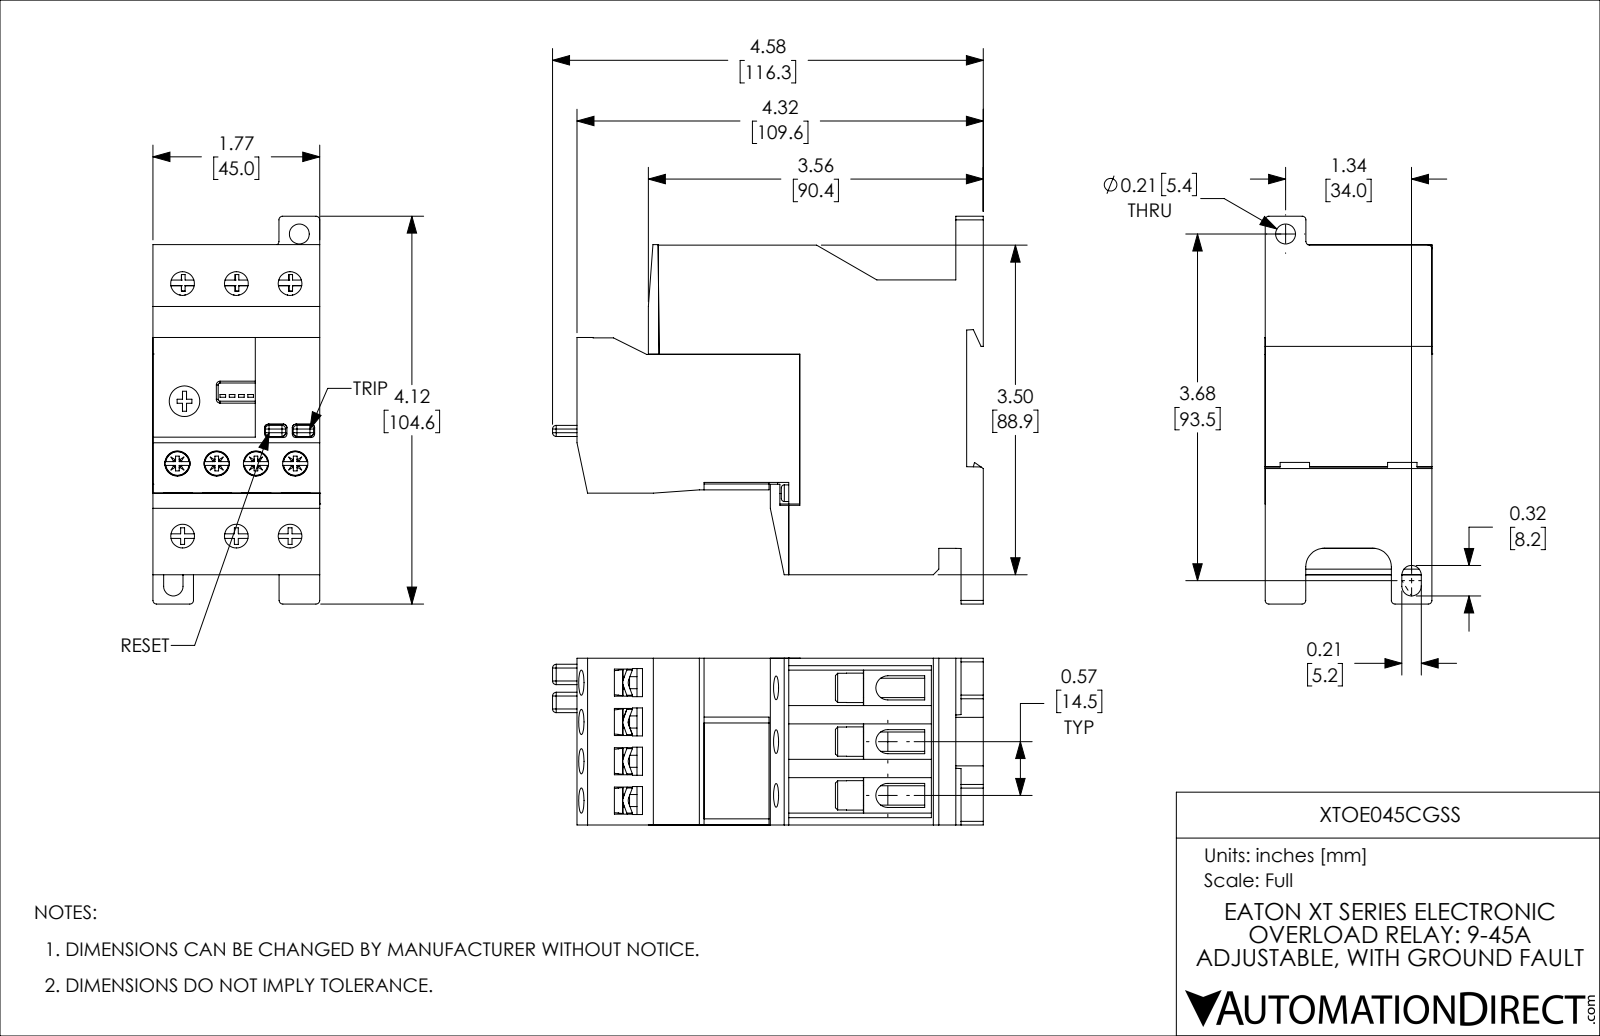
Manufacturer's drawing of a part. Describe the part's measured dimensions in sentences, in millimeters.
The part is named "XTOE045CGSS". Its 3-D file was written by "SolidWorks 2018 (AUTOMOTIVE_DESIGN)". It is 42 solids with 1296 faces: 854 planar, 281 cylindrical and 161 other. Overall it measures 116.25 by 104.6 by 45.01 millimeters. Its volume is 292 500 cubic millimeters and its surface area 75 869 square millimeters. Round holes: 6 of diameter 6.4, 5 of diameter 3.55, 4 of diameter 6.8, 3 of diameter 7.94, 2 of diameter 2.18, 2 of diameter 3.2, 1 of diameter 5.38. Round bosses or shafts: 4 of diameter 3.4, 4 of diameter 3.25, 4 of diameter 2.8, 4 of diameter 2.5, 3 of diameter 8, 2 of diameter 4.5, 1 of diameter 8.27. Partial cylindrical surfaces (rounded edges, fillets, slot ends): 64 of radius 0.5, 24 of radius 0.3, 22 of radius 1, 10 of radius 2, 6 of radius 3.25, 4 of radius 0.8, 3 of radius 0.4, 2 of radius 1.57. The main face-to-face distances are 45, 14.5, 1.87, 10.89, 4.5, 45.01, 44.99, 29, 49.5, 16.37. The hole center spacings are 10.6, 21.2, 10.59, 10.61, 19.63, 48.55, 48.82, 51.07.
